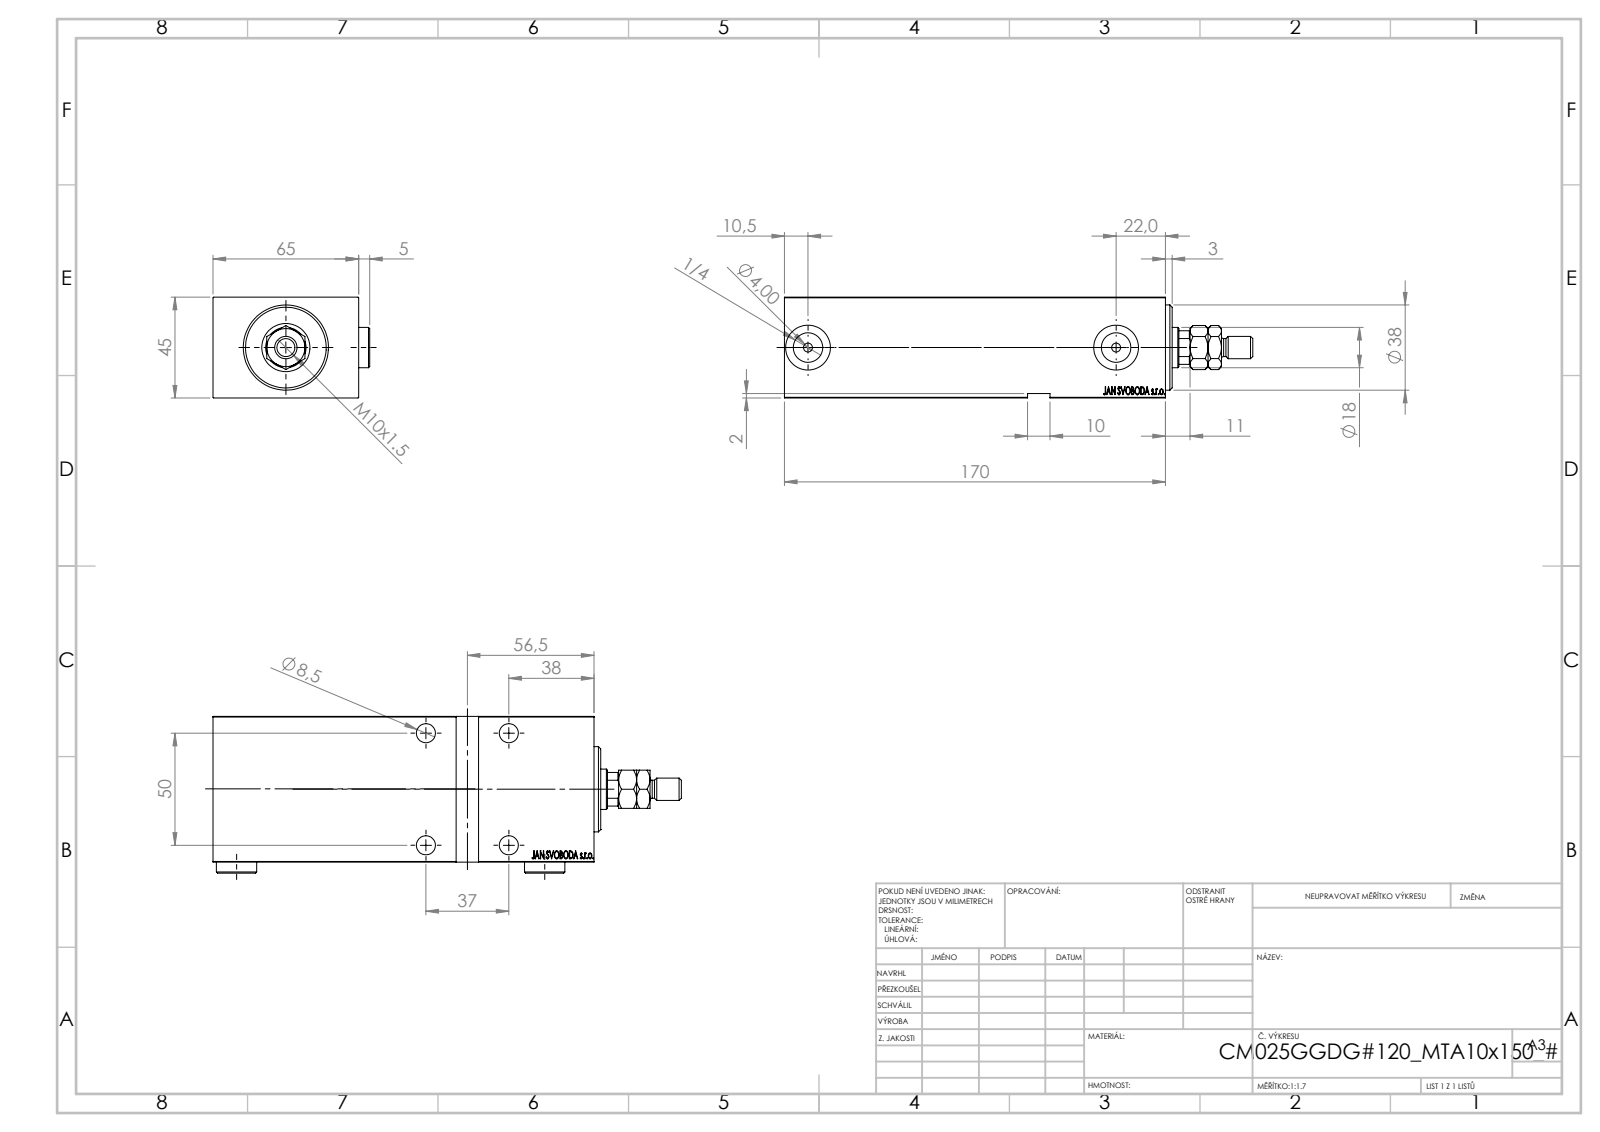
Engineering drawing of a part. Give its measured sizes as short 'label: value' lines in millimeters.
name: MTA; Zatka_OIL_PORT; V450CM_VC_G; V450CM_G_Body (+1 more)
written by: SolidWorks 2019 (CONFIG_CONTROL_DESIGN)
unit: mm
bodies: 6 solids, 962 faces (460 planar, 74 cylindrical, 428 other)
size: 209 × 69.9 × 45
volume: 456 552 mm³; area: 83 314 mm²
holes: 5× ⌀8.5, 4× ⌀13.5, 2× ⌀4, 2× ⌀13.16, 2× ⌀20, 1× ⌀18, 1× ⌀21.5, 1× ⌀25, 1× ⌀27, 1× ⌀35
bosses: 2× ⌀18, 1× ⌀38, 1× ⌀10, 1× ⌀8
rounds: 1× R8.5
face distances: 45, 65, 170, 6, 64.9, 159, 5, 8, 164, 11
hole spacings: 37, 50, 62.2, 137.5
